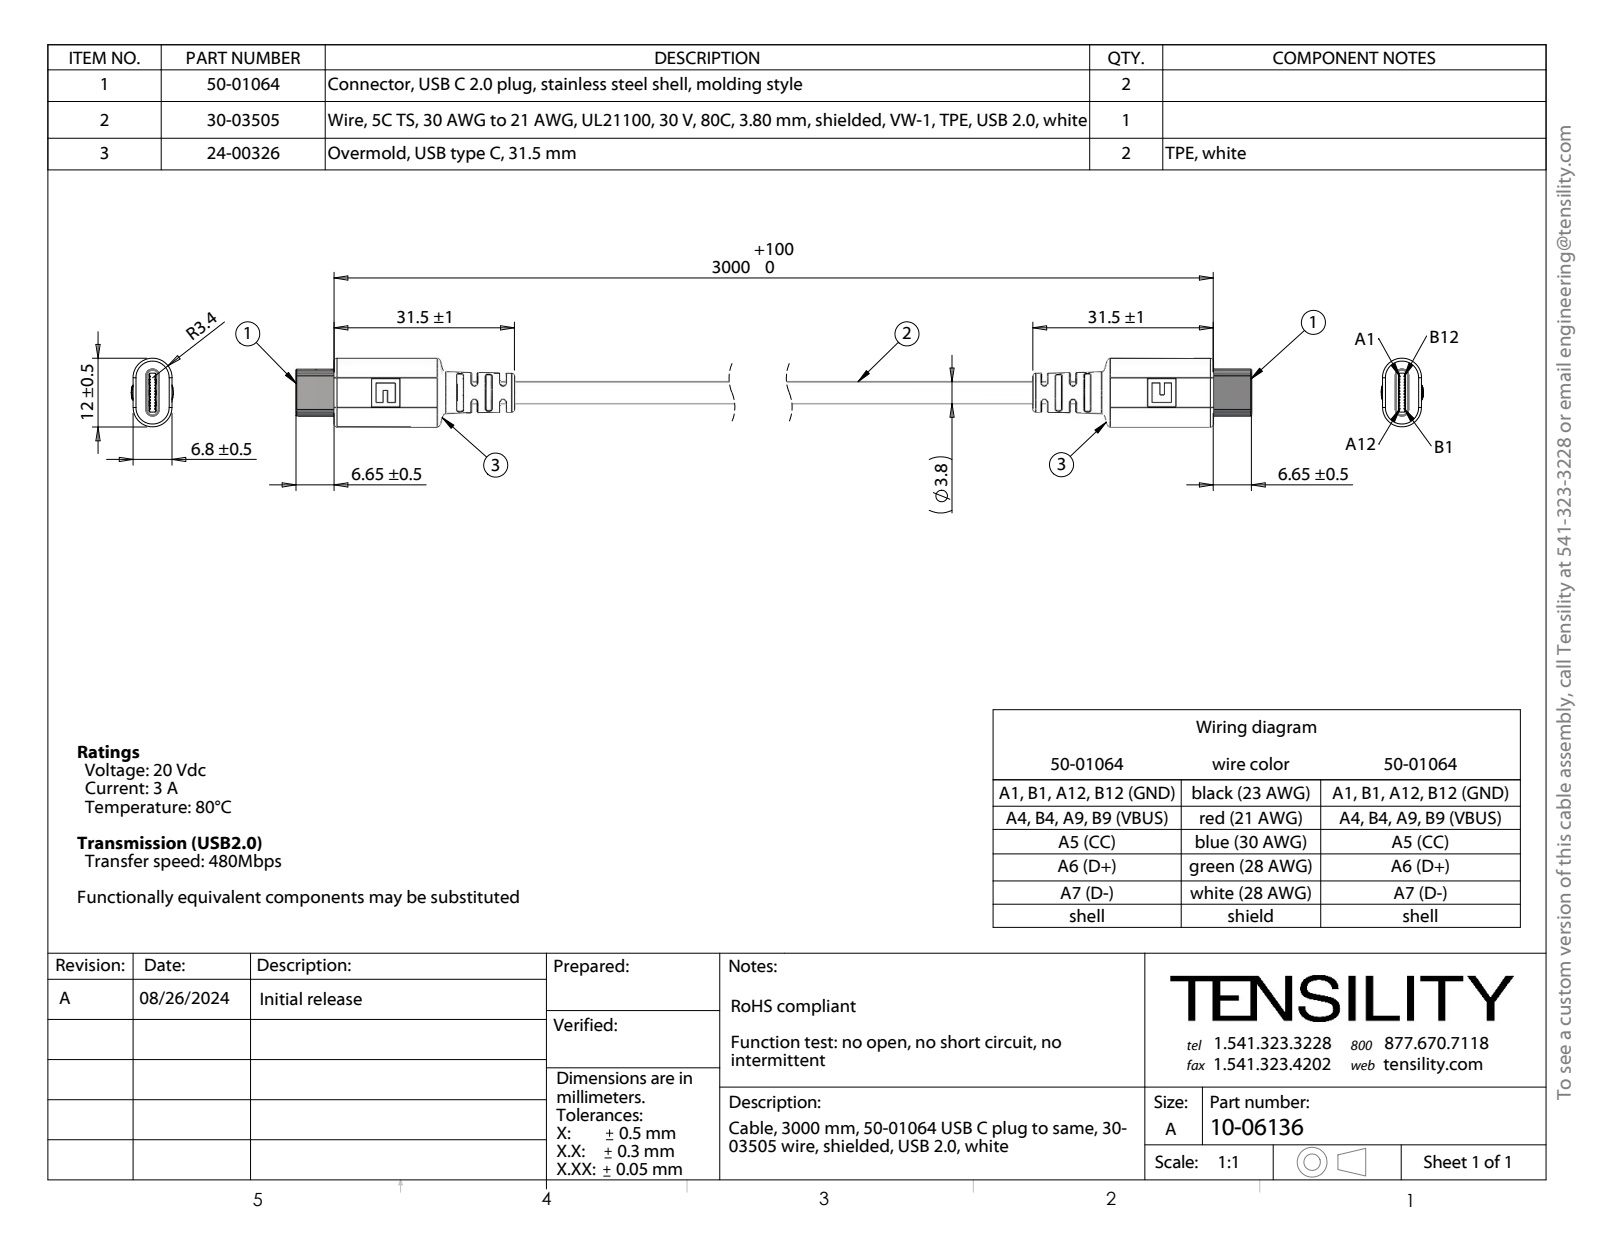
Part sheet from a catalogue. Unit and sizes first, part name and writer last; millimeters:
Units: millimetres
Overall size (bounding box): 206.3 × 12 × 7.38
Round holes (diameter × count): ⌀2.73 ×1, ⌀2.76 ×1, ⌀2.98 ×1
Round bosses / shafts (diameter × count): ⌀0.83 ×2, ⌀3.8 ×1, ⌀2.96 ×1, ⌀2.75 ×1, ⌀1.2 ×1, ⌀1 ×1, ⌀0.55 ×1
Partial cylindrical surfaces — rounded edges, fillets, slot ends (radius × count): R0.5 ×20, R0.1 ×4, R0.15 ×4, R0.25 ×4, R0.6 ×2, R1.18 ×2, R3.4 ×2
Main face-to-face distances: 6.8, 2.5, 4.57, 2.23, 2.35, 0.65, 1.7, 2.22, 4.58, 1
Hole centre spacings: 0.43, 0.33, 0.32, 0.49, 0.42, 0.58, 0.44, 0.56
Volume: 5 080 mm³ · Surface area: 20 593 mm²
Bodies: 55 solids, 1076 faces (496 planar, 352 cylindrical, 228 other)
Part name (STEP PRODUCT): 30-03505_blunt cut; 10-06136; 50-01064_Hidden emarker; 24-00326
STEP written by: SolidWorks 2021 (CONFIG_CONTROL_DESIGN)
